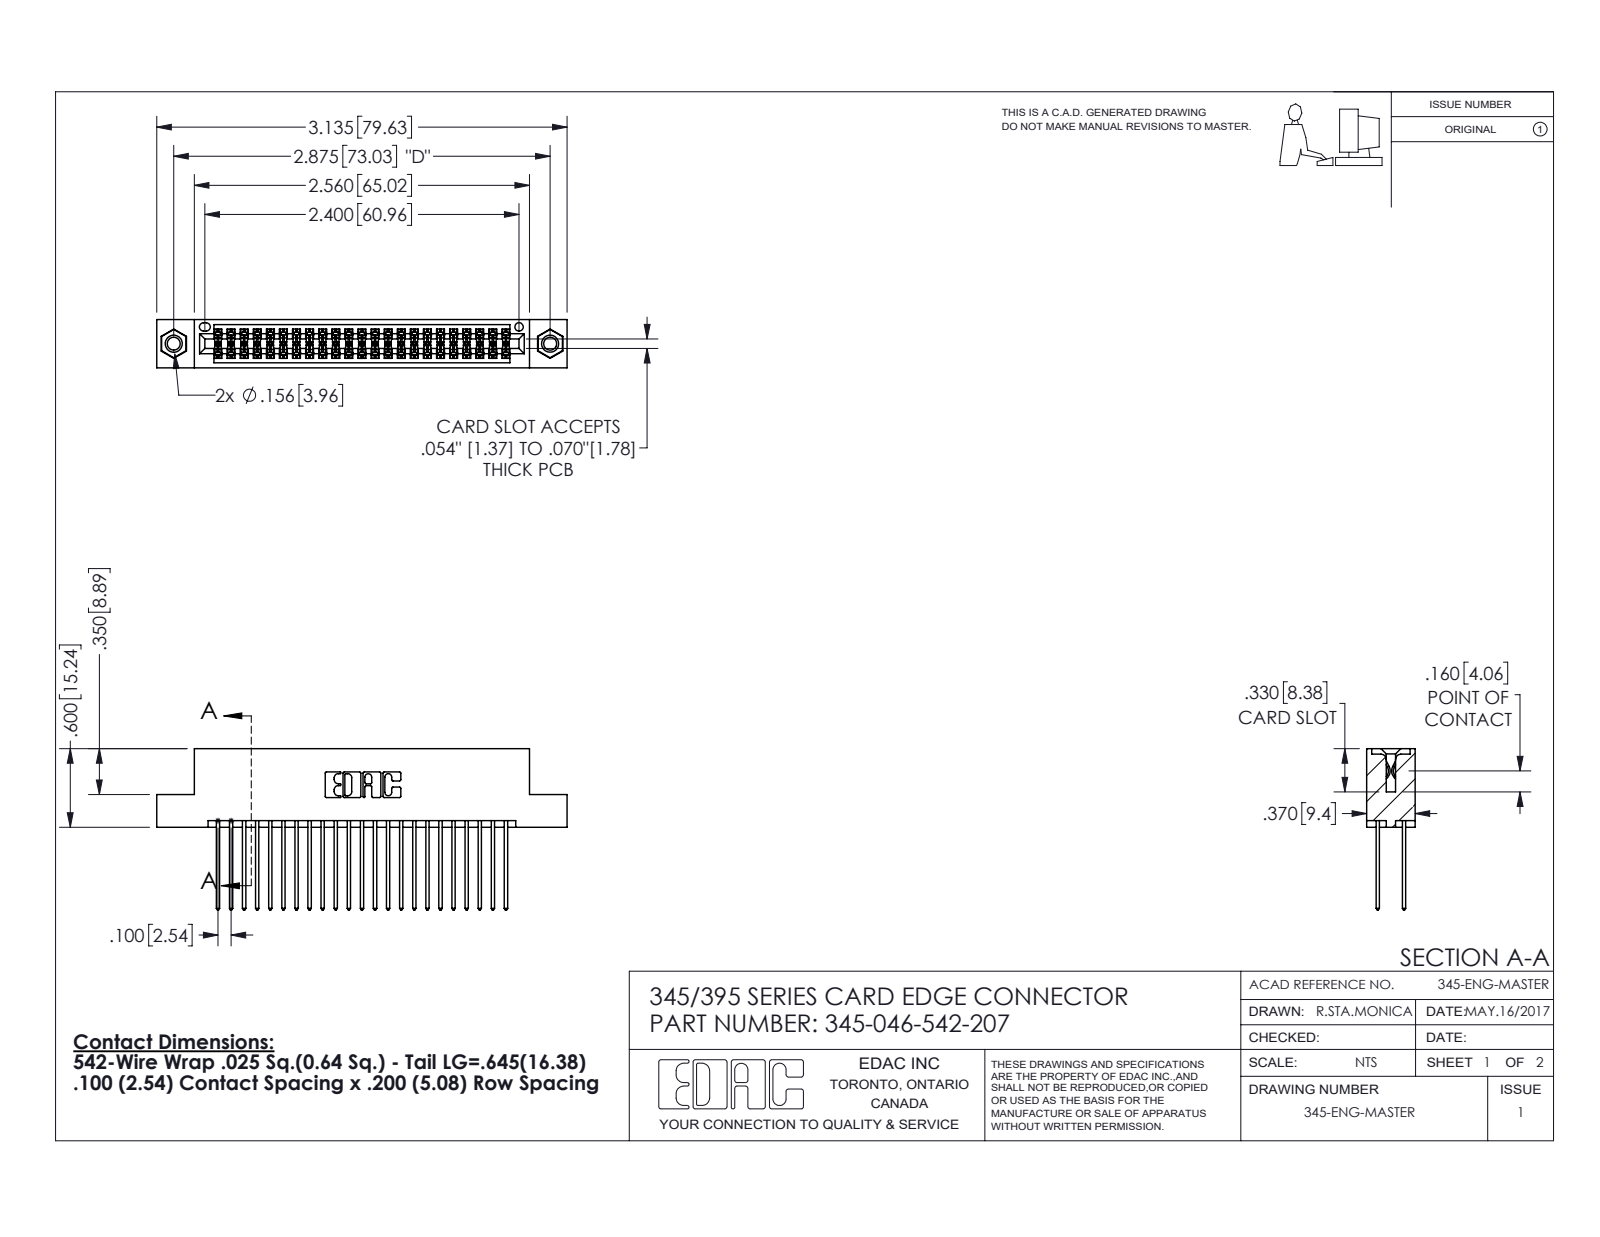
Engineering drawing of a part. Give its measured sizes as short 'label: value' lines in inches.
name: 345-250-001_345-250-005-103; 345-046-542-207; 345-292-001_345-293-142; 345 Part_Flush Mounting Lugs - 0.156 Dia-TI
written by: SolidWorks 2016 (CONFIG_CONTROL_DESIGN)
unit: in
bodies: 49 solids, 2486 faces (1630 planar, 840 cylindrical, 16 other)
size: 3.135 × 1.232 × 0.37
volume: 0.474 in³; area: 18.81 in²
holes: 2× ⌀0.098, 2× ⌀0.125, 2× ⌀0.156, 1× ⌀0.064
bosses: 2× ⌀0.155
rounds: 69× R0.006, 46× R0.01, 22× R0.01, 6× R0.007, 6× R0.031, 3× R0.026, 2× R0.014, 2× R0.019
face distances: 0.072, 0.298, 0.2, 0.098, 0.272, 0.025, 0.37, 0.225, 0.175, 0.149
hole spacings: 0.27, 2.641, 2.875
